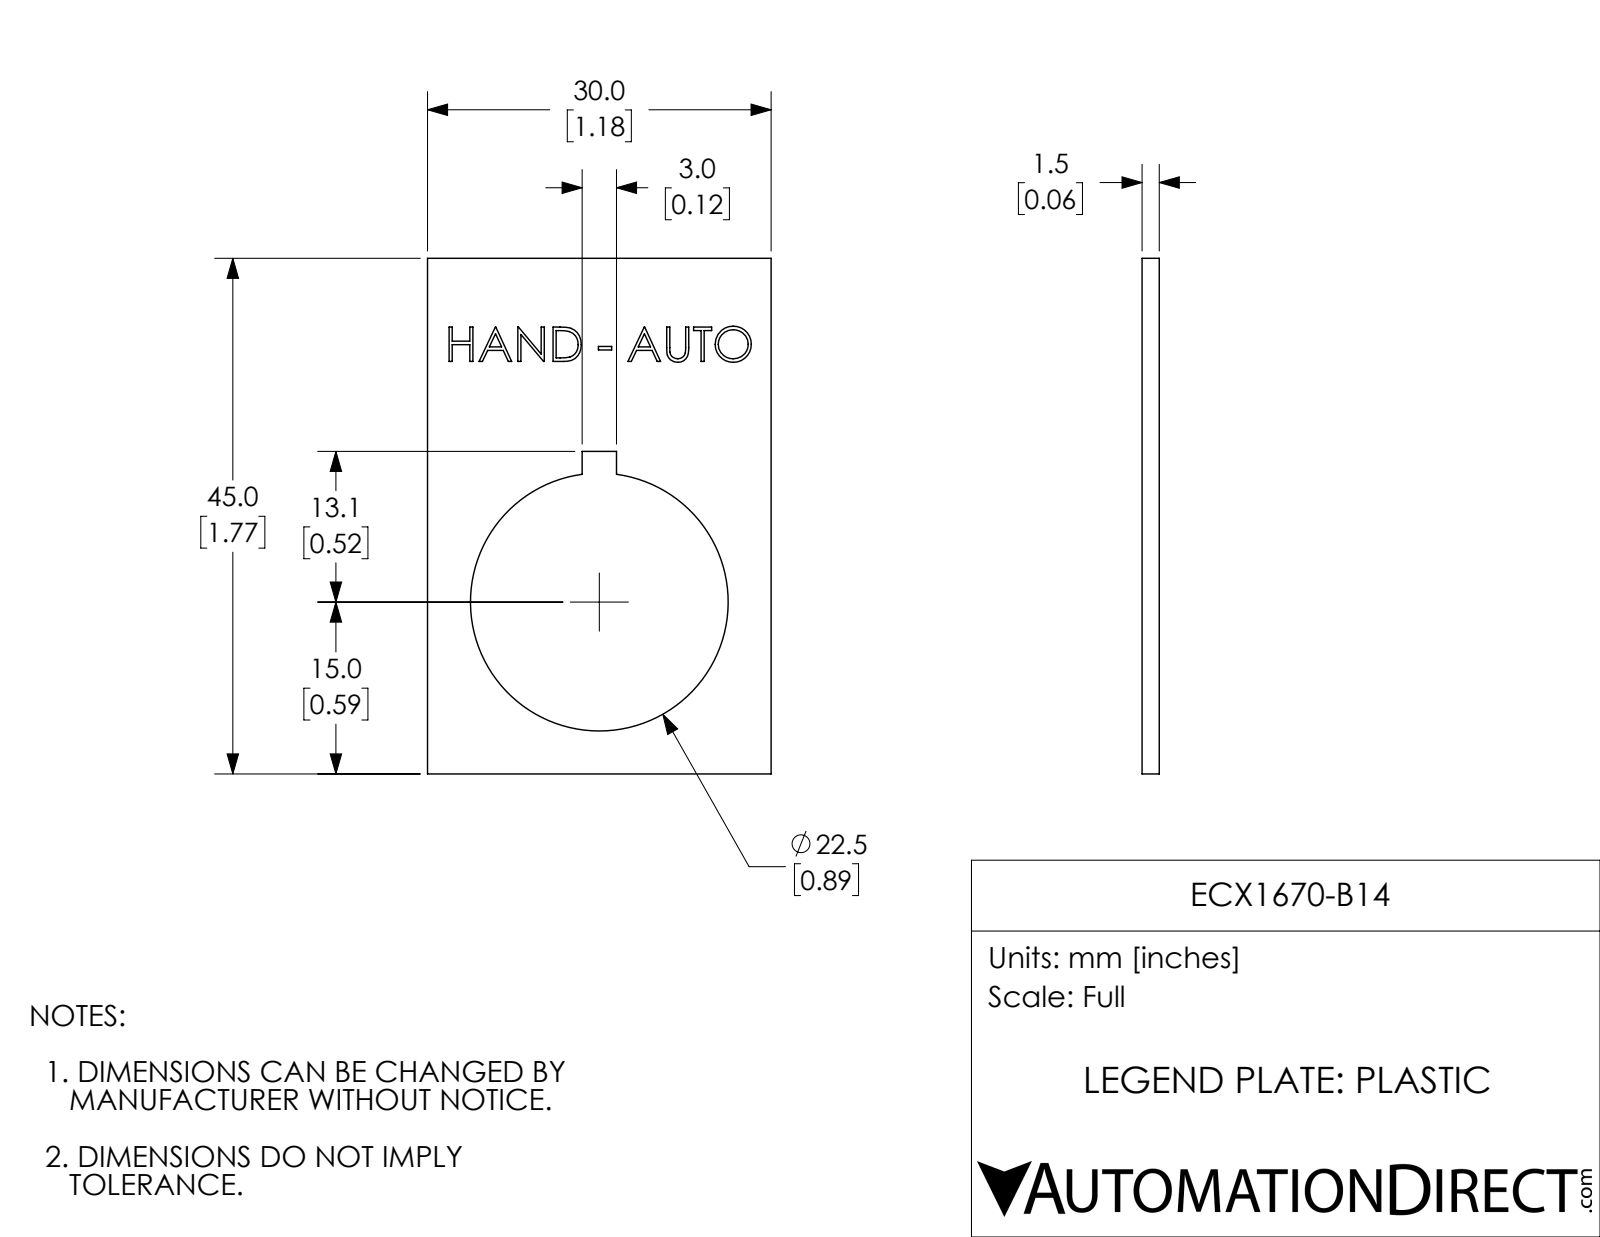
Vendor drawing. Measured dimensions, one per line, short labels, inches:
name: ECX1670-B14
written by: SolidWorks 2017 (AUTOMOTIVE_DESIGN)
unit: in
bodies: 1 solid, 115 faces (90 planar, 3 cylindrical, 22 other)
size: 1.772 × 1.181 × 0.059
volume: 0.087 in³; area: 3.462 in²
holes: 1× ⌀0.886
face distances: 0.059, 1.181, 1.772, 0.058, 0.531, 0.65, 1.108, 0.663, 0.118, 0.236
